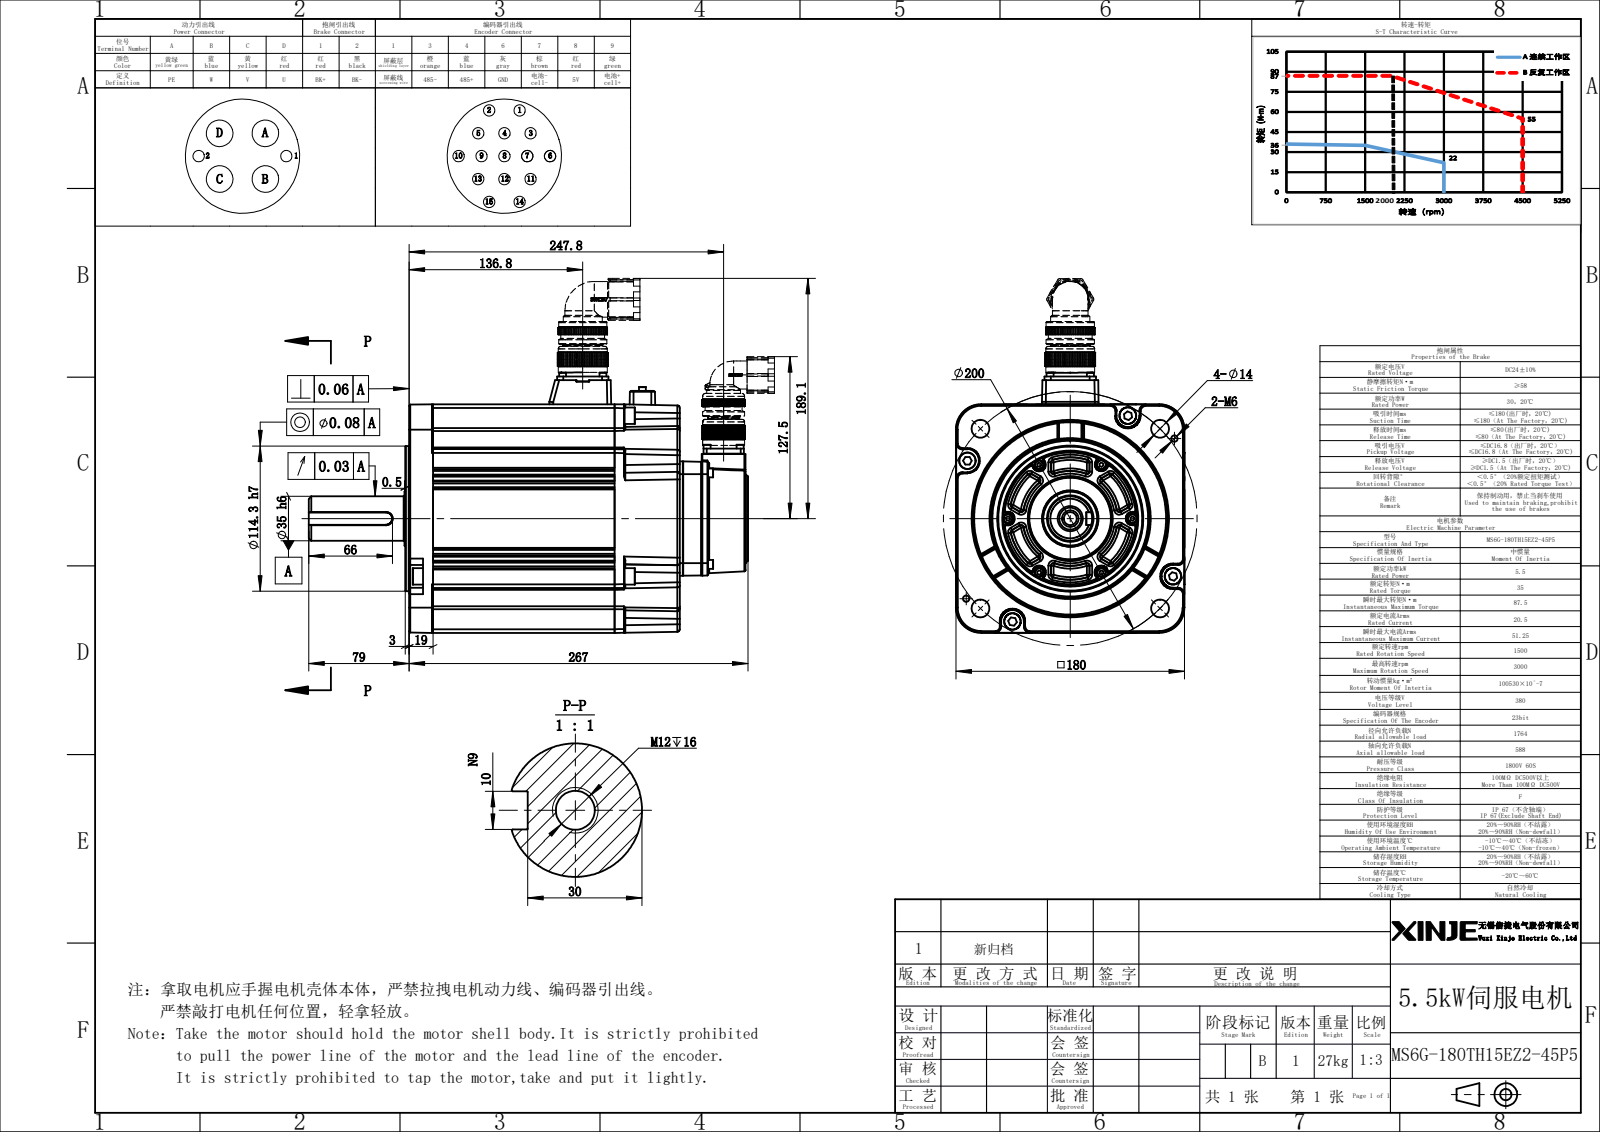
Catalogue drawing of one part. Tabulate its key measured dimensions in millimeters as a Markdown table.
| quantity | value |
| --- | --- |
| part name | MS6G-180TH15EZ2-45P5 |
| STEP written by | SolidWorks 2022 (CONFIG_CONTROL_DESIGN) |
| units | millimeters |
| bodies | 43 solids, 4116 faces (1825 planar, 986 cylindrical, 1305 other) |
| overall size | 346 × 221.1 × 180 |
| volume | 6 318 000 mm³ |
| surface area | 509 003 mm² |
| round holes (diameter × count) | 1.5 × 15, 4.5 × 10, 2.5 × 7, 3.2 × 7, 6.8 × 6, 3.3 × 4, 3.7 × 4, 4 × 4, 5.45 × 4, 9 × 4, 11 × 4, 14 × 4 |
| round bosses / shafts (diameter × count) | 2.5 × 15, 2 × 15, 3 × 11, 7 × 10, 4 × 10, 5.5 × 8, 13 × 4, 8 × 4 |
| partial cylindrical surfaces (radius × count) | 1 × 80, 3 × 41, 2 × 30, 2.5 × 20, 0.5 × 18, 0.2 × 17, 6 × 16, 5 × 13 |
| main face-to-face distances | 142.8, 180, 2.7, 51.5, 5, 197, 54.2, 194.3, 9, 2 |
| hole center spacings | 49, 16.04, 10.4, 21.08, 3.83, 112.25, 3.6, 5 |
